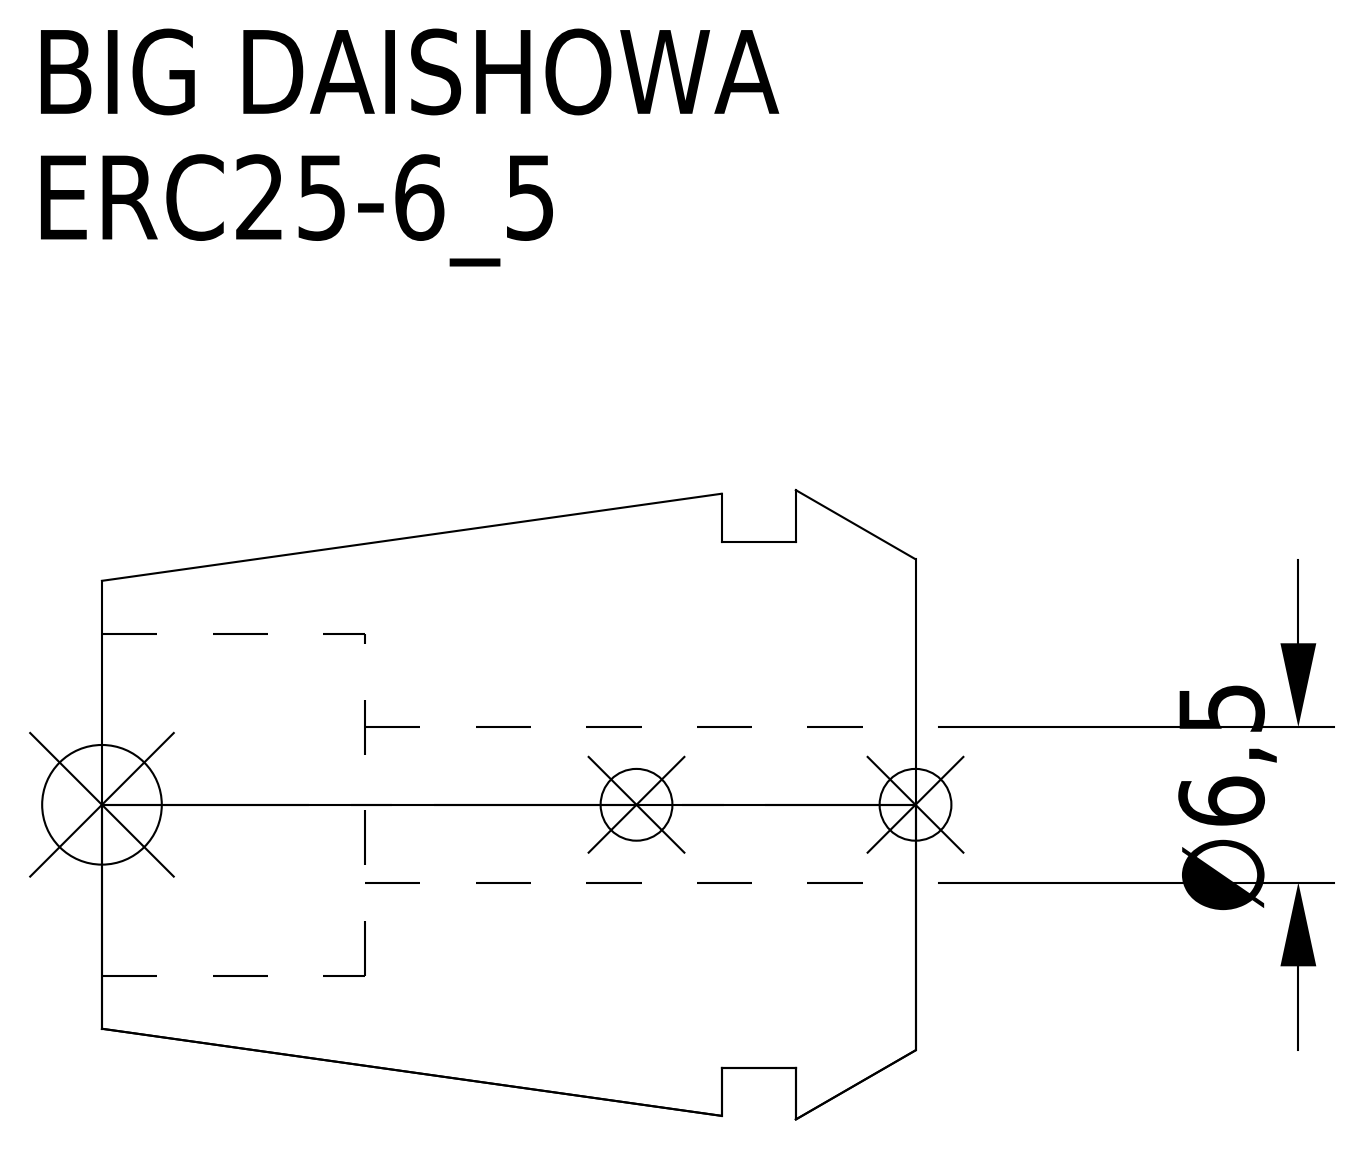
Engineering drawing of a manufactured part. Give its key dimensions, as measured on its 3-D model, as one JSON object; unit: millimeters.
{"part_name": "ERC25-6_5", "step_written_by": "CREO PARAMETRIC BY PTC INC, 2016380 (AUTOMOTIVE_DESIGN)", "units": "millimeters", "bodies": {"solids": 1, "faces": 15, "planar": 5, "cylindrical": 6, "other": 4}, "overall_size": [34, 26.3, 26.3], "volume_mm3": 11073, "surface_area_mm2": 4294, "round_holes": [[6.5, 1], [14.3, 1]], "round_bosses_or_shafts": [[22, 1]], "face_to_face_distances": [5, 8.1, 3.1, 23, 18, 14.9, 34, 29, 25.9, 11]}
